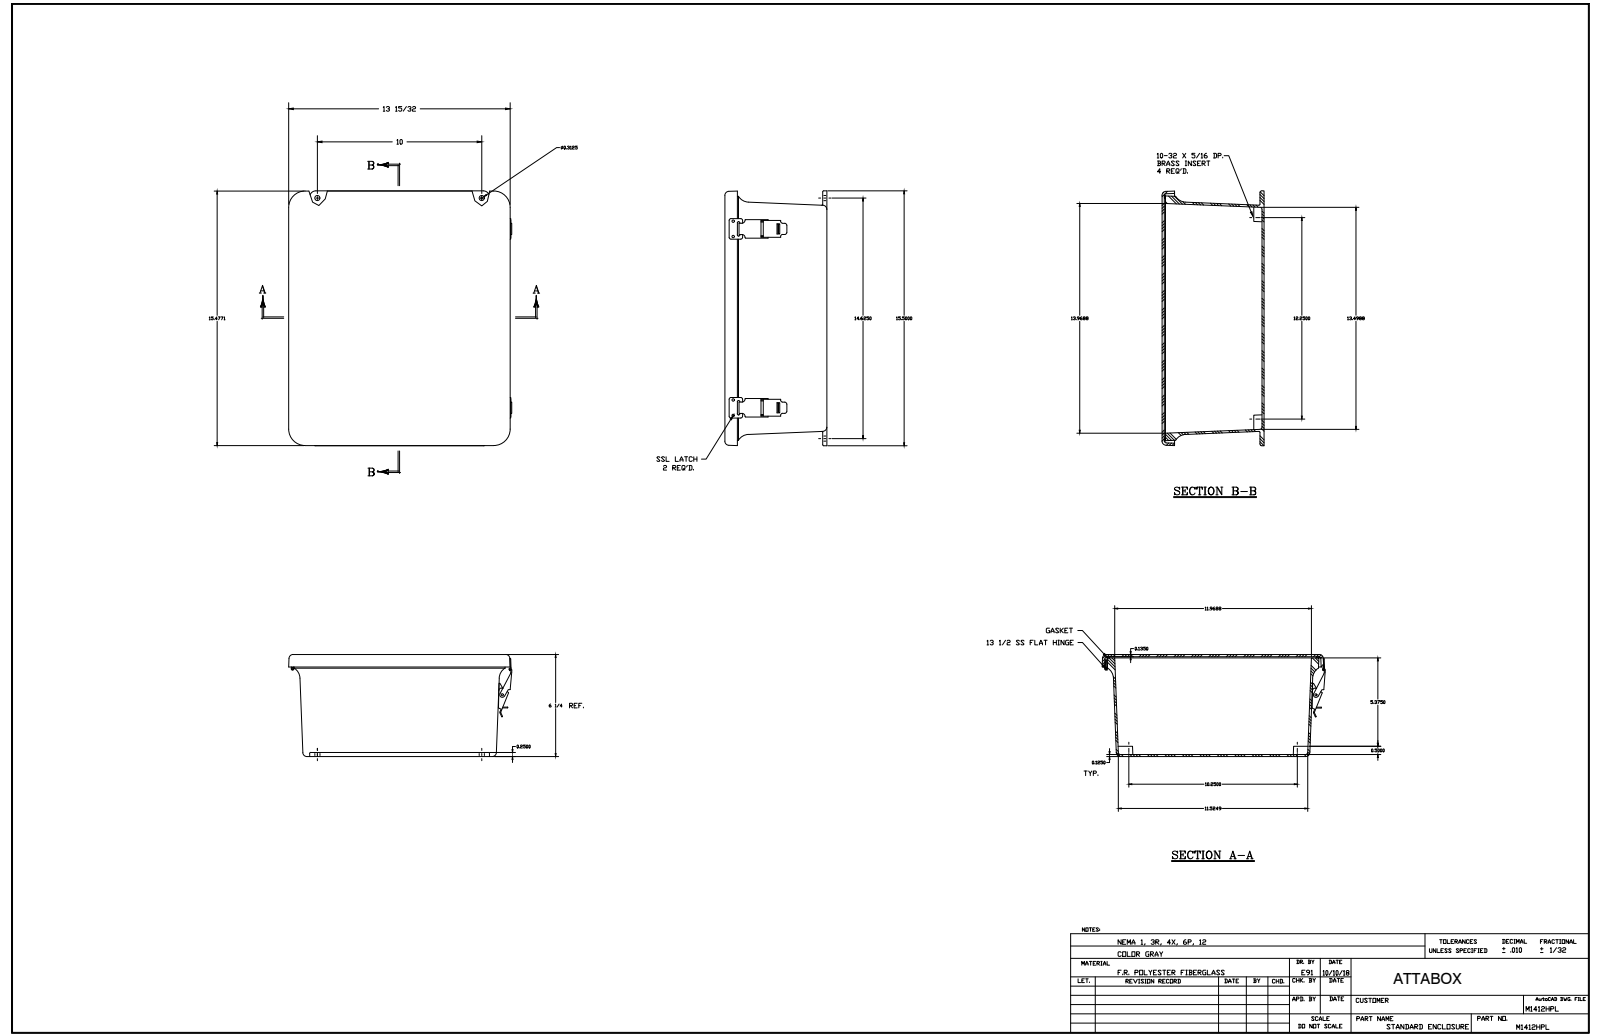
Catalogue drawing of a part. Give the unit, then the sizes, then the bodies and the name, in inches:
Units: inches
Overall size (bounding box): 15.5 × 13.566 × 6.213
Round holes (diameter × count): ⌀0.14 ×22, ⌀0.131 ×10, ⌀0.104 ×8, ⌀0.152 ×8, ⌀0.13 ×4, ⌀0.156 ×4, ⌀0.218 ×4, ⌀0.135 ×2, ⌀0.375 ×2, ⌀0.085 ×1, ⌀0.085 ×1, ⌀0.135 ×1
Round bosses / shafts (diameter × count): ⌀0.125 ×11, ⌀0.25 ×10, ⌀0.125 ×7, ⌀0.27 ×4, ⌀0.3 ×1, ⌀0.17 ×1, ⌀0.155 ×1, ⌀0.155 ×1
Partial cylindrical surfaces — rounded edges, fillets, slot ends (radius × count): R0.015 ×20, R0.031 ×20, R0.125 ×20, R0.045 ×16, R0.03 ×12, R0.25 ×12, R0.023 ×8, R0.06 ×6
Main face-to-face distances: 0.125, 0.135, 6.078, 6.213, 5.952, 6.087, 0.125, 0.33, 0.152, 5.875
Hole centre spacings: 3.25, 10.882, 6.5, 10.908, 0.25, 0.75, 9.75, 10.881
Volume: 113.7 in³ · Surface area: 1 603 in²
Bodies: 40 solids, 1046 faces (457 planar, 440 cylindrical, 149 other)
Part name (STEP PRODUCT): M1412HPL
STEP written by: SolidWorks 2018 (AUTOMOTIVE_DESIGN)
